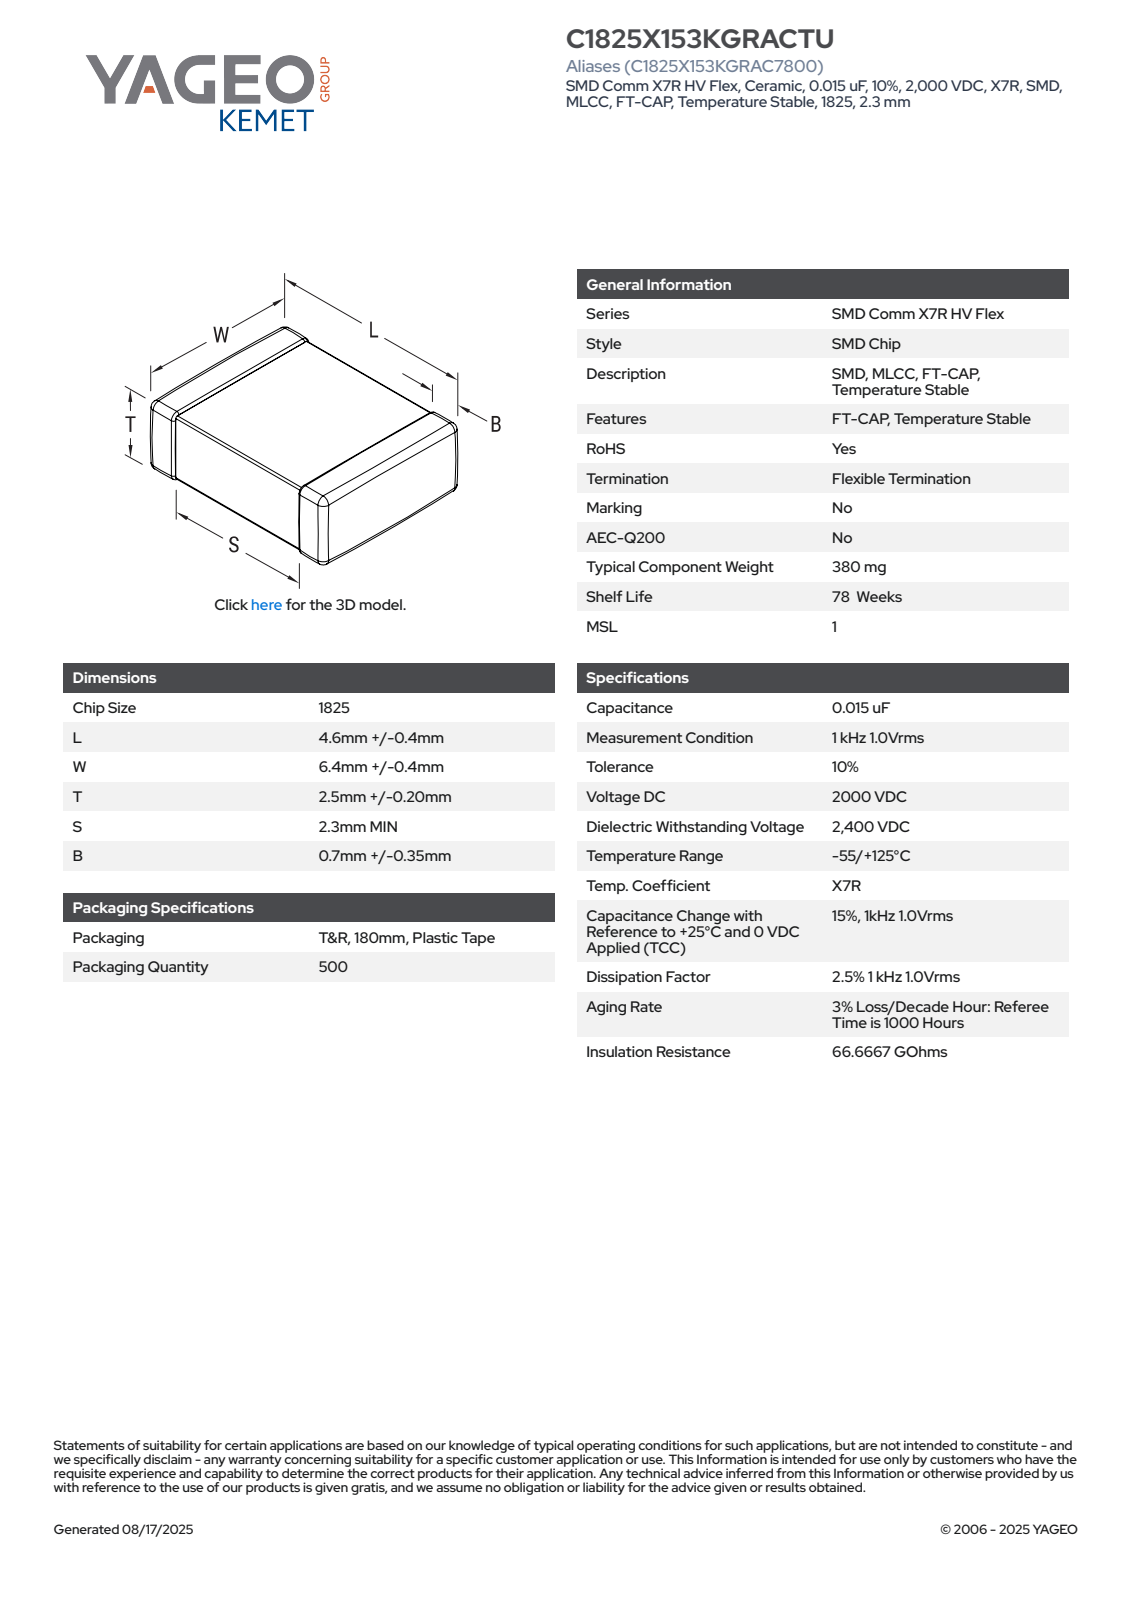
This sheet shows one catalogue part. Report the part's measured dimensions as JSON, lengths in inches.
{"part_name": "CCS_CCSTD_1825_L5W6.8T2.7B0.7", "step_written_by": "SolidWorks 2021 (AUTOMOTIVE_DESIGN)", "units": "inches", "bodies": {"solids": 4, "faces": 121, "planar": 71, "cylindrical": 34, "other": 16}, "overall_size": [0.268, 0.197, 0.106], "volume_in3": 0.005, "surface_area_in2": 0.208, "partial_cylinders_radius": [[0.006, 24]], "face_to_face_distances": [0.101, 0.095, 0.197, 0.106, 0.262, 0.257, 0.268, 0.039, 0.091, 0.067]}
